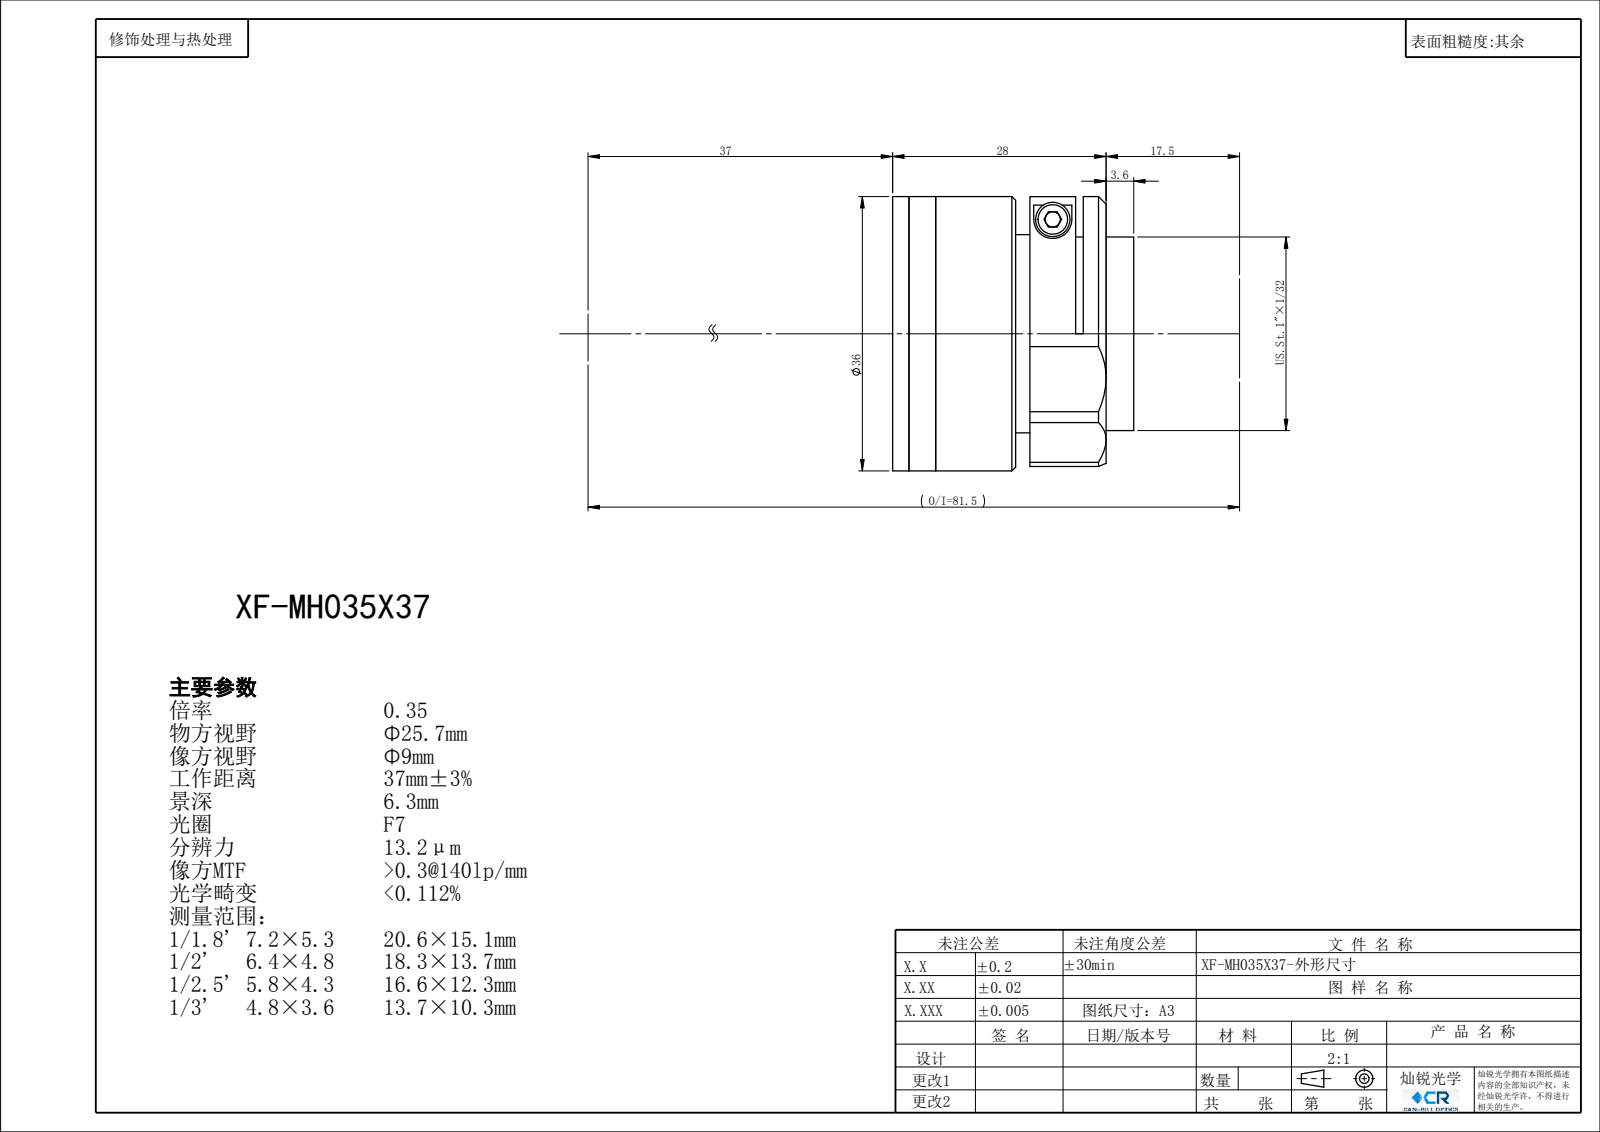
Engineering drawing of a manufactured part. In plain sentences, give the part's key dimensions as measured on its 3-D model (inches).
The part is named "XF-MH035X37". Its 3-D file was written by "SolidWorks 2018 (CONFIG_CONTROL_DESIGN)". It is 3 solids with 165 faces: 62 planar, 84 cylindrical and 19 other. Overall it measures 1.417 by 1.417 by 1.246 inches. Its volume is 1.208 cubic inches and its surface area 22.04 square inches. Round holes: 1 of diameter 0.081, 1 of diameter 0.118, 1 of diameter 0.276, 1 of diameter 0.291, 1 of diameter 0.331, 1 of diameter 0.394, 1 of diameter 0.472, 1 of diameter 0.551, 1 of diameter 0.63, 1 of diameter 0.709, 1 of diameter 0.827, 1 of diameter 0.866. Round bosses or shafts: 1 of diameter 1.417, 1 of diameter 1.181, 1 of diameter 1.102, 1 of diameter 1, 1 of diameter 0.921, 1 of diameter 0.787, 1 of diameter 0.177, 1 of diameter 0.098. Partial cylindrical surfaces (rounded edges, fillets, slot ends): 5 of radius 0.984, 1 of radius 0.098, 1 of radius 0.205. The main face-to-face distances are 0.276, 0.138, 0.625, 0.35, 0.079, 0.085, 0.71, 0.197, 0.36, 0.074.
